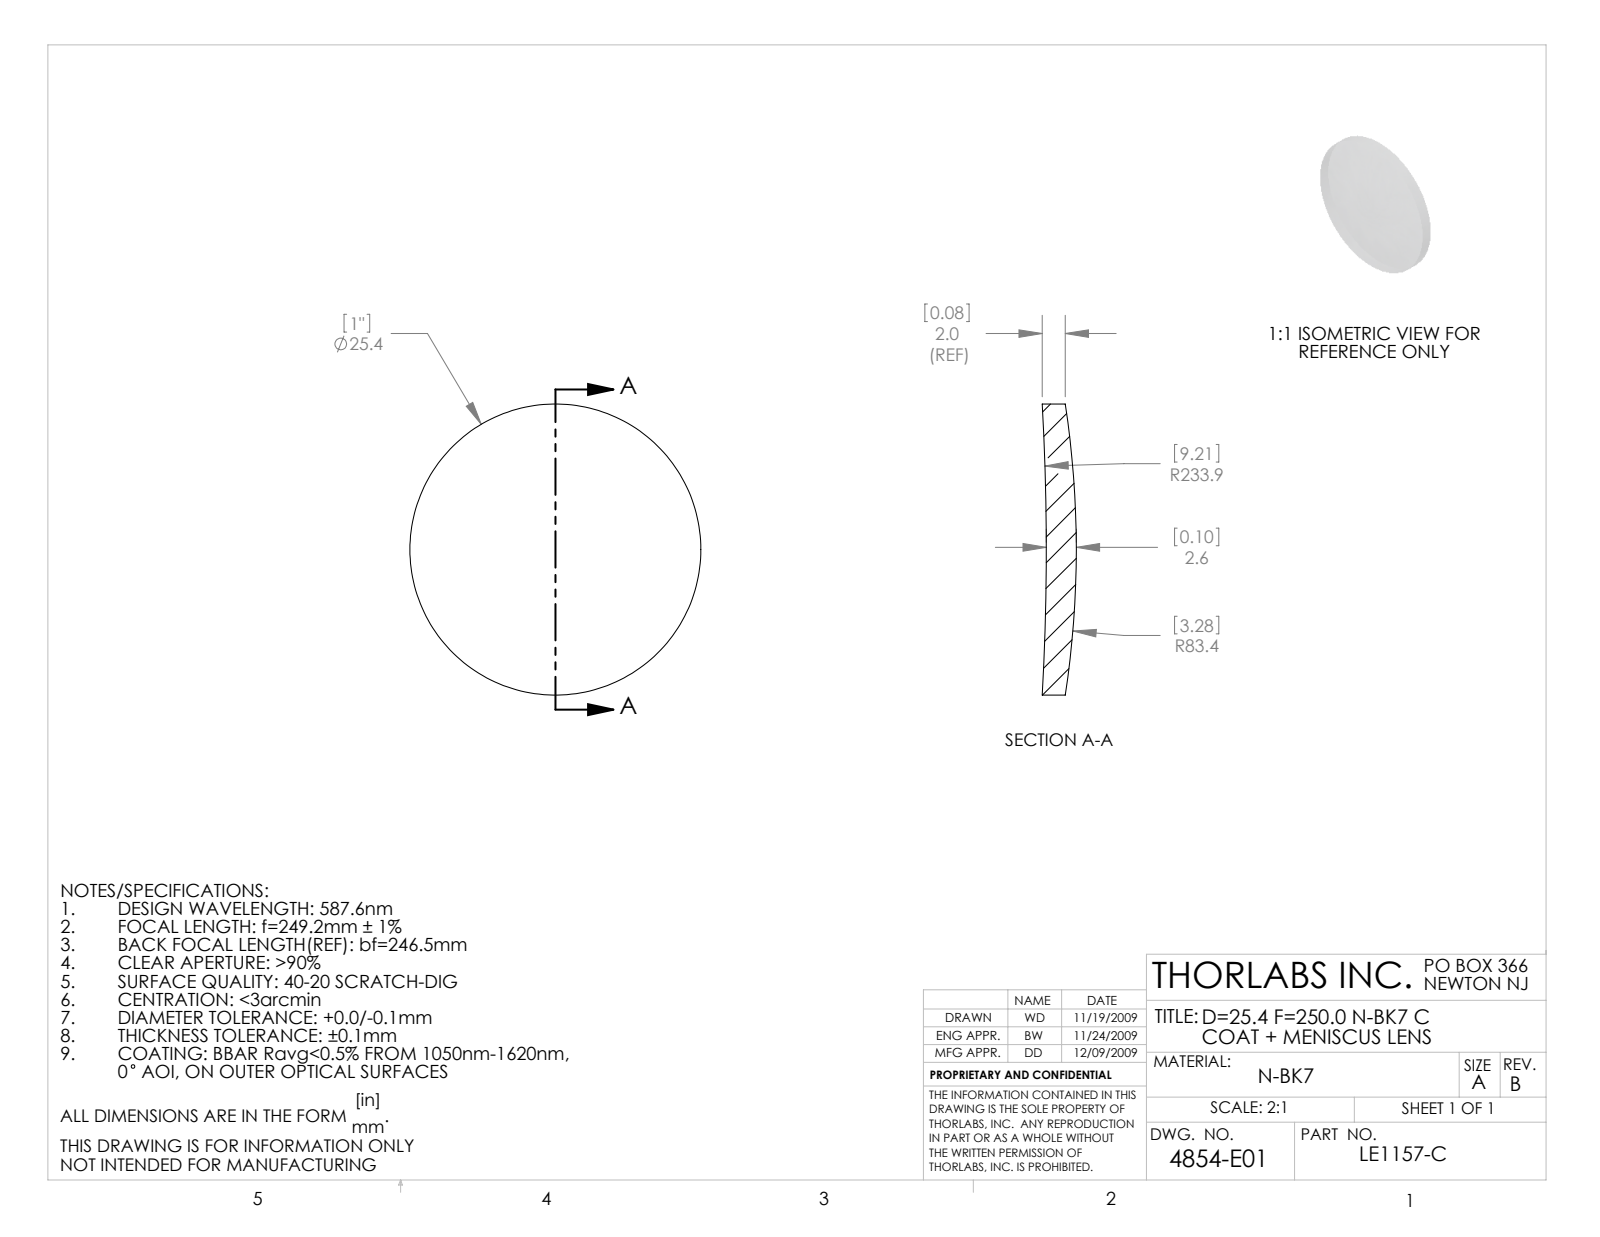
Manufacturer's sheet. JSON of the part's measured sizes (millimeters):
{"part_name": "4854-E0W", "step_written_by": "SolidWorks 2009 (AUTOMOTIVE_DESIGN)", "units": "millimeters", "bodies": {"solids": 1, "faces": 6, "planar": 0, "cylindrical": 2, "other": 4}, "overall_size": [25.4, 25.4, 2.98], "volume_mm3": 1174, "surface_area_mm2": 1177, "round_bosses_or_shafts": [[25.4, 1]]}
